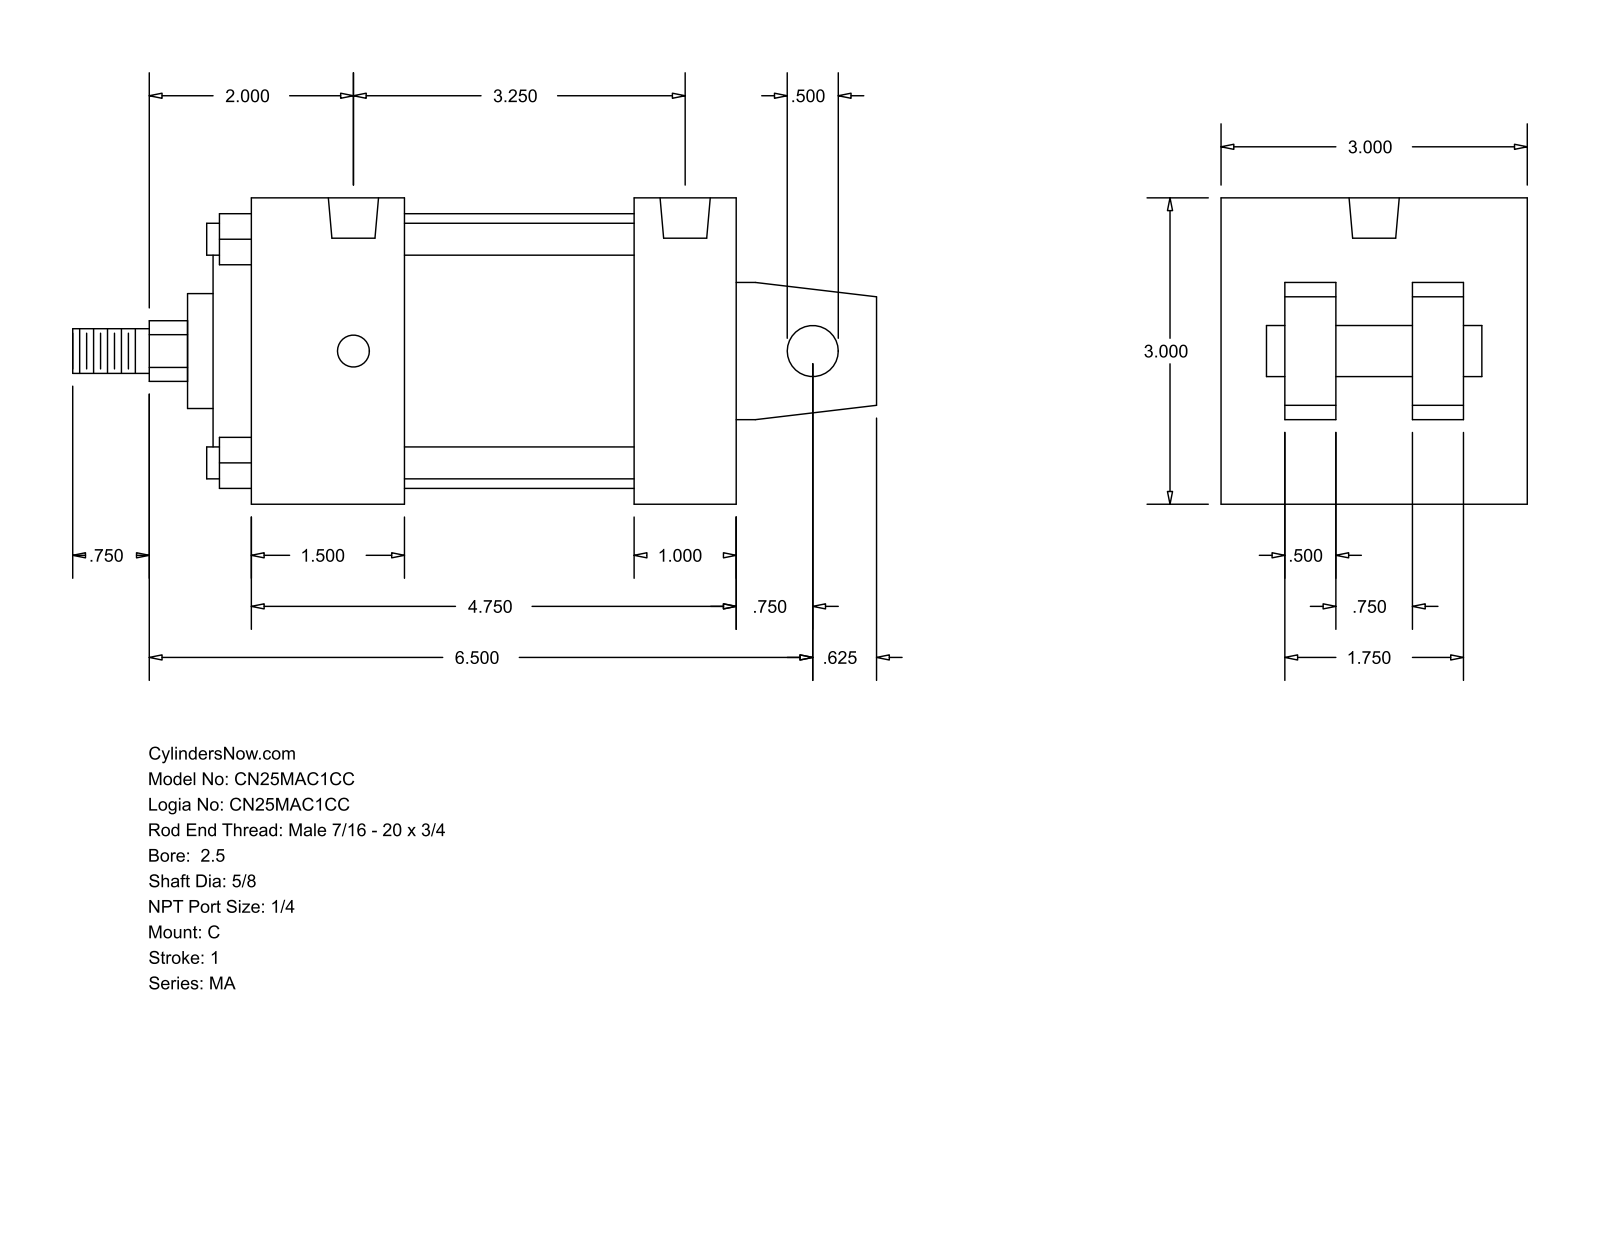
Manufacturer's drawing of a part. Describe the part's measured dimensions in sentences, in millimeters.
The part is named "MA_C__0250_0.625". Its 3-D file was written by "GSSL Pune (CONFIG_CONTROL_DESIGN)". It is 0 solids with 105 faces: 77 planar, 28 cylindrical and 0 other. Overall it measures 200.03 by 76.2 by 76.2 millimeters. Round holes: 4 of diameter 7.94, 2 of diameter 12.49. Round bosses or shafts: 4 of diameter 7.94, 1 of diameter 68.33, 1 of diameter 50.8, 1 of diameter 28.57, 1 of diameter 15.88, 1 of diameter 12.7, 1 of diameter 11.11. Partial cylindrical surfaces (rounded edges, fillets, slot ends): 1 of radius 7.54. The main face-to-face distances are 76.2, 120.65, 12.7, 15.87, 47.63, 25.4, 82.55, 57.15, 38.1, 95.25. The hole center spacings are 82.55.
